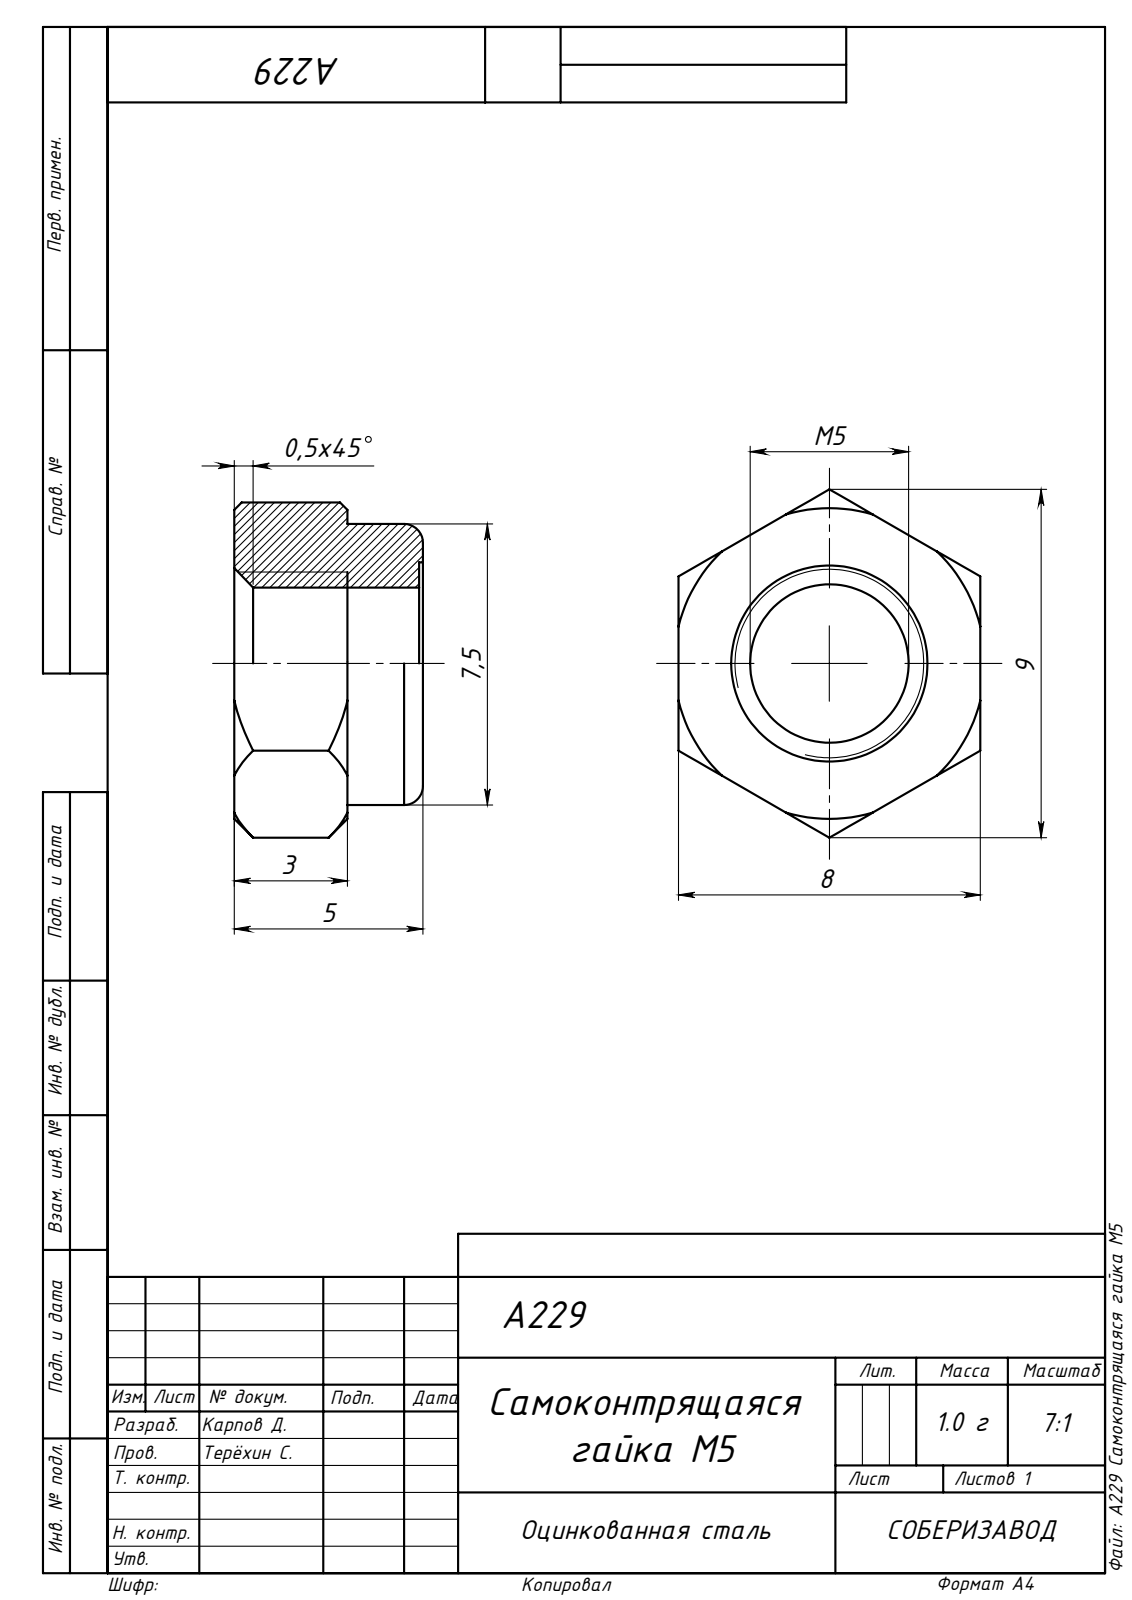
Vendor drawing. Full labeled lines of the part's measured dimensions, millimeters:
Part name (STEP PRODUCT): A229 Самоконтрящаяся гайка M5
STEP written by: SolidWorks 2019 (AUTOMOTIVE_DESIGN)
Units: millimetres
Bodies: 1 solid, 32 faces (10 planar, 6 cylindrical, 16 other)
Overall size (bounding box): 9.24 × 8 × 5
Volume: 181 mm³ · Surface area: 267 mm²
Round holes (diameter × count): ⌀4.2 ×1, ⌀5.5 ×1
Round bosses / shafts (diameter × count): ⌀7.5 ×1
Main face-to-face distances: 8, 4.9, 5, 3, 1.9, 2
